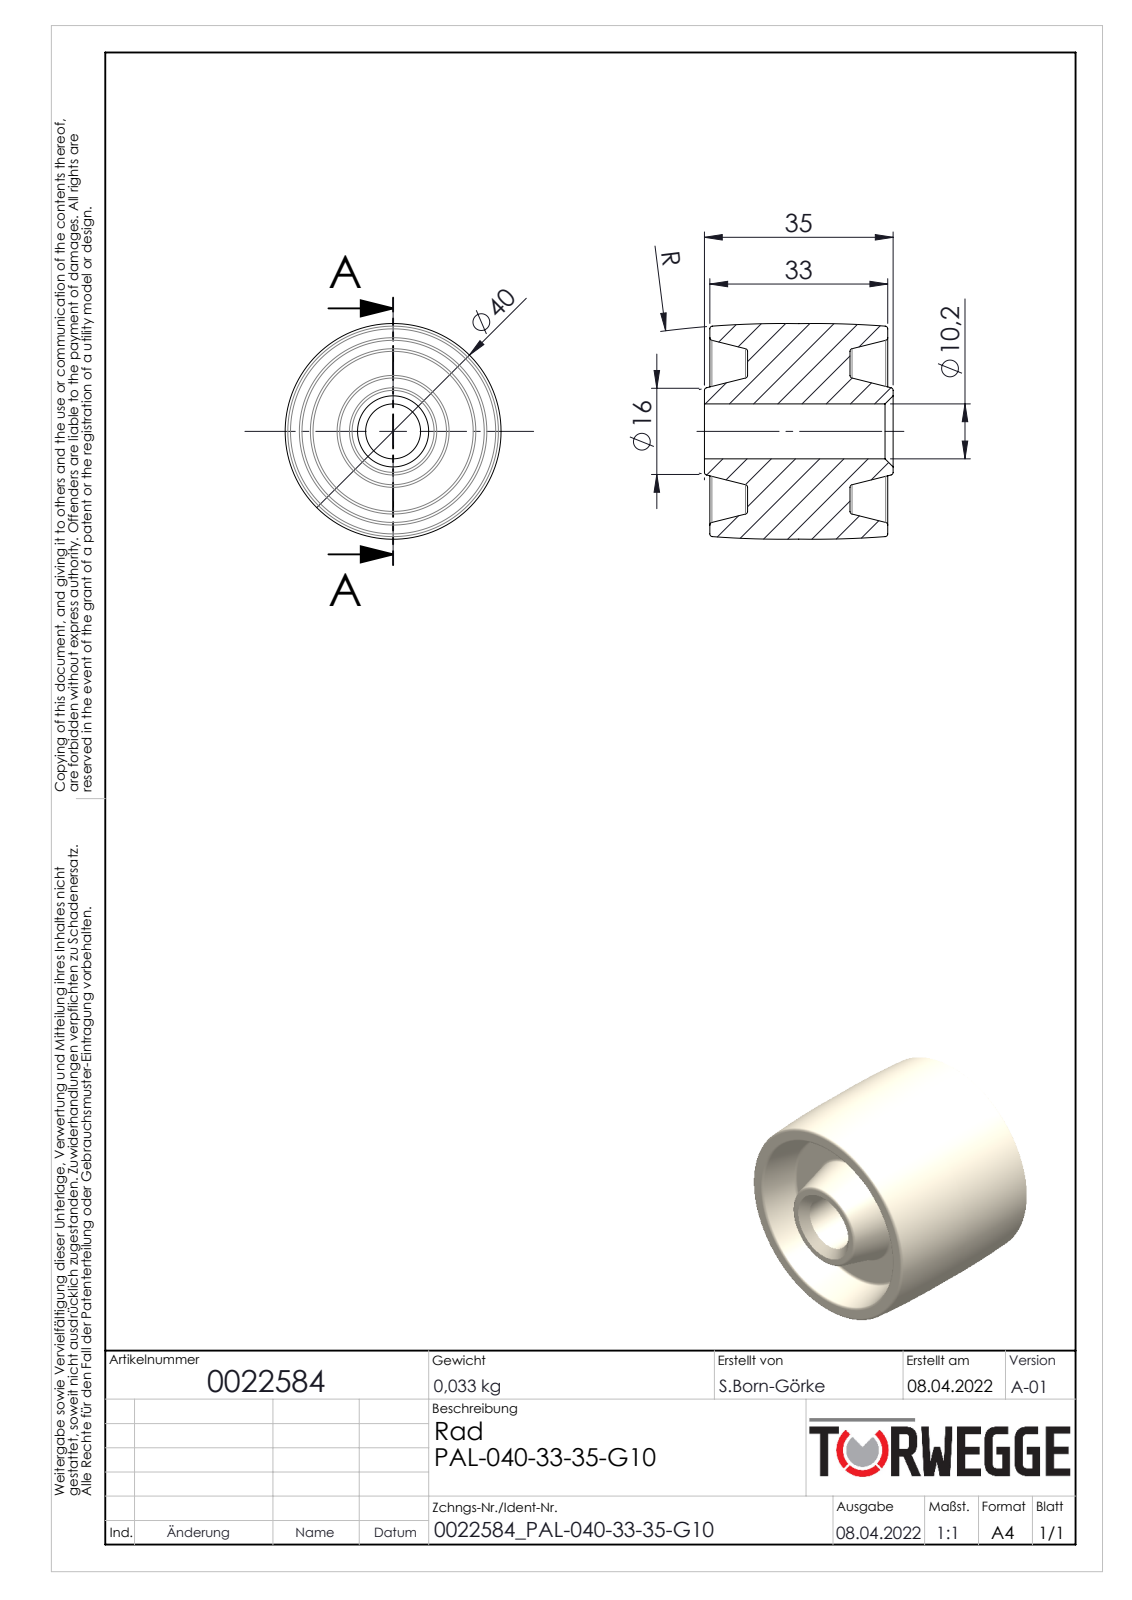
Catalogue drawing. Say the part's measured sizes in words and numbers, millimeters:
The part is named "0022584". Its 3-D file was written by "SolidWorks 2020 (AUTOMOTIVE_DESIGN)". It is 1 solid with 42 faces: 6 planar, 2 cylindrical and 34 other. Overall it measures 40.05 by 40.05 by 35 millimeters. Its volume is 30 706 cubic millimeters and its surface area 9 143 square millimeters. Round holes: 1 of diameter 10.2. The main face-to-face distances are 7, 26, 19, 33, 1, 8, 27, 34, 35.
